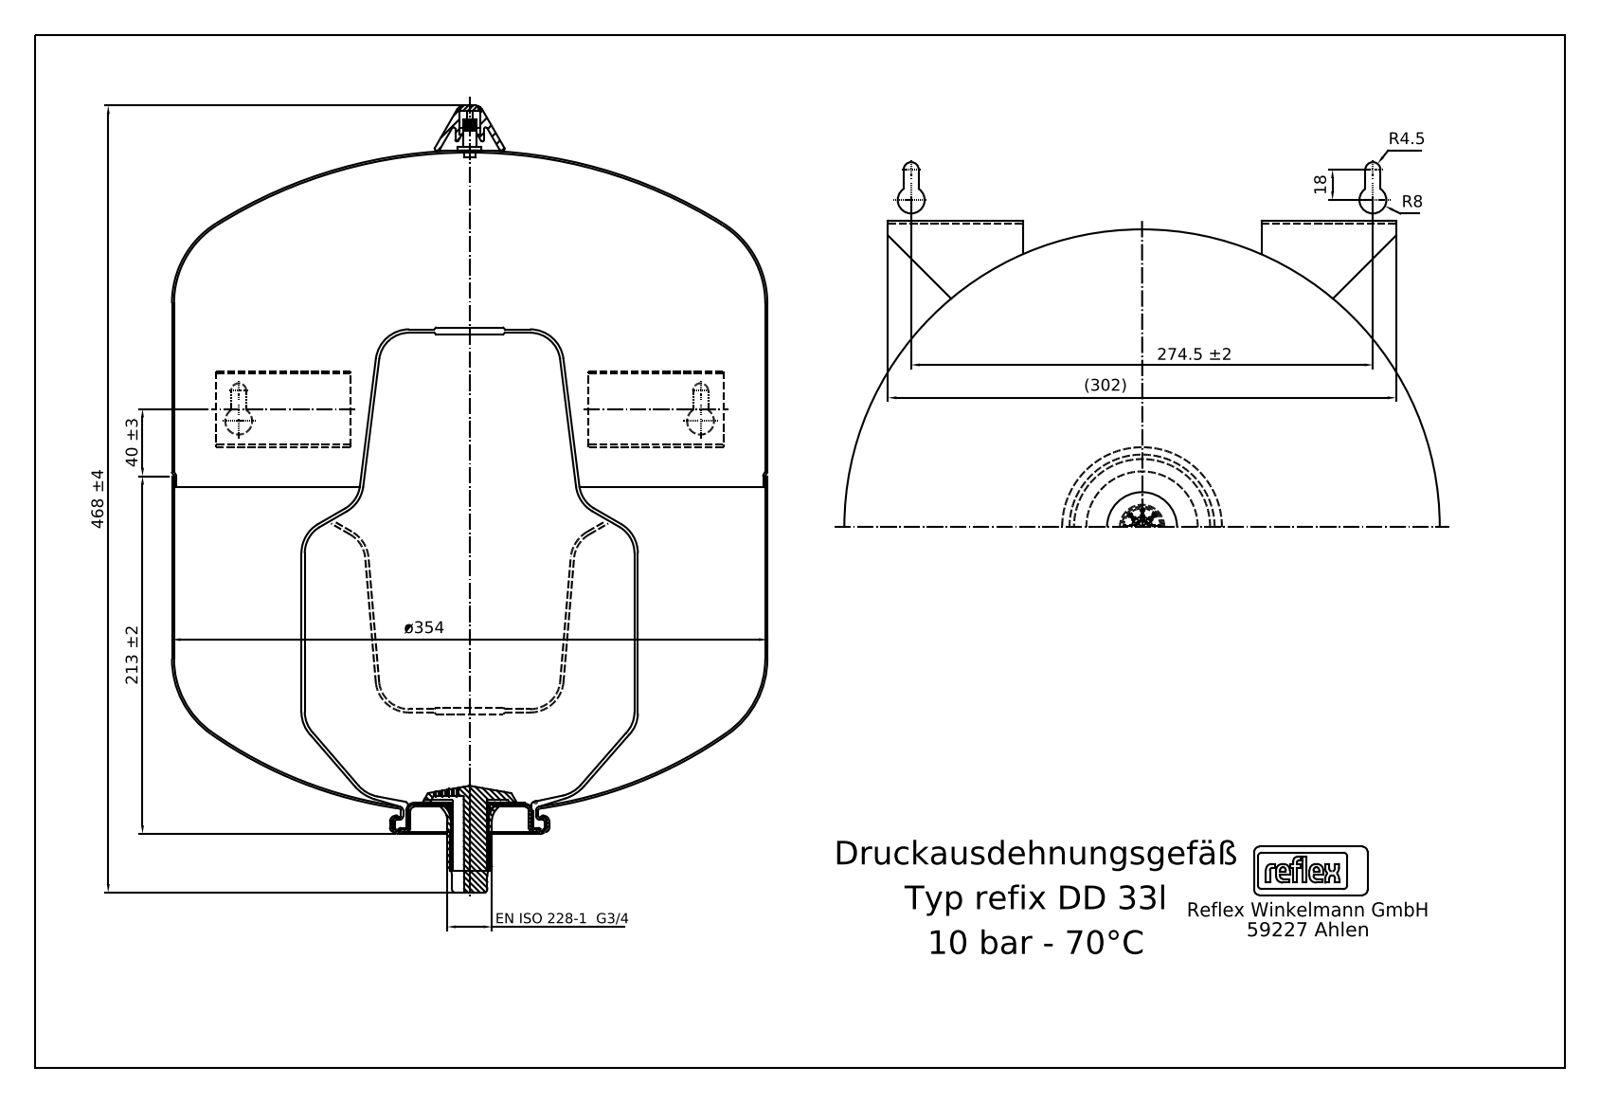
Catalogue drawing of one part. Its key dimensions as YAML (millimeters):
step_written_by: "Mechanical Desktop 2011 (CONFIG_CONTROL_DESIGN)"
units: millimeters
bodies: {solids: 17, faces: 342, planar: 182, cylindrical: 102, other: 58}
overall_size: [472, 360.3, 354]
volume: 32550000
surface_area: 993110
round_holes:
  - {diameter: 14.1, count: 1}
  - {diameter: 16, count: 1}
  - {diameter: 18.9, count: 1}
round_bosses_or_shafts:
  - {diameter: 354, count: 1}
  - {diameter: 96, count: 1}
  - {diameter: 82, count: 1}
  - {diameter: 26.9, count: 1}
  - {diameter: 17.1, count: 1}
  - {diameter: 9, count: 1}
  - {diameter: 6, count: 1}
partial_cylinders:
  - {radius: 1.49, count: 4}
  - {radius: 2.24, count: 4}
  - {radius: 2.35, count: 4}
  - {radius: 4, count: 4}
  - {radius: 4.05, count: 4}
  - {radius: 1.52, count: 2}
  - {radius: 2, count: 2}
  - {radius: 2.24, count: 2}
face_to_face_distances: [212, 2, 84, 296, 13, 97, 309, 43, 1.5, 206.5]
